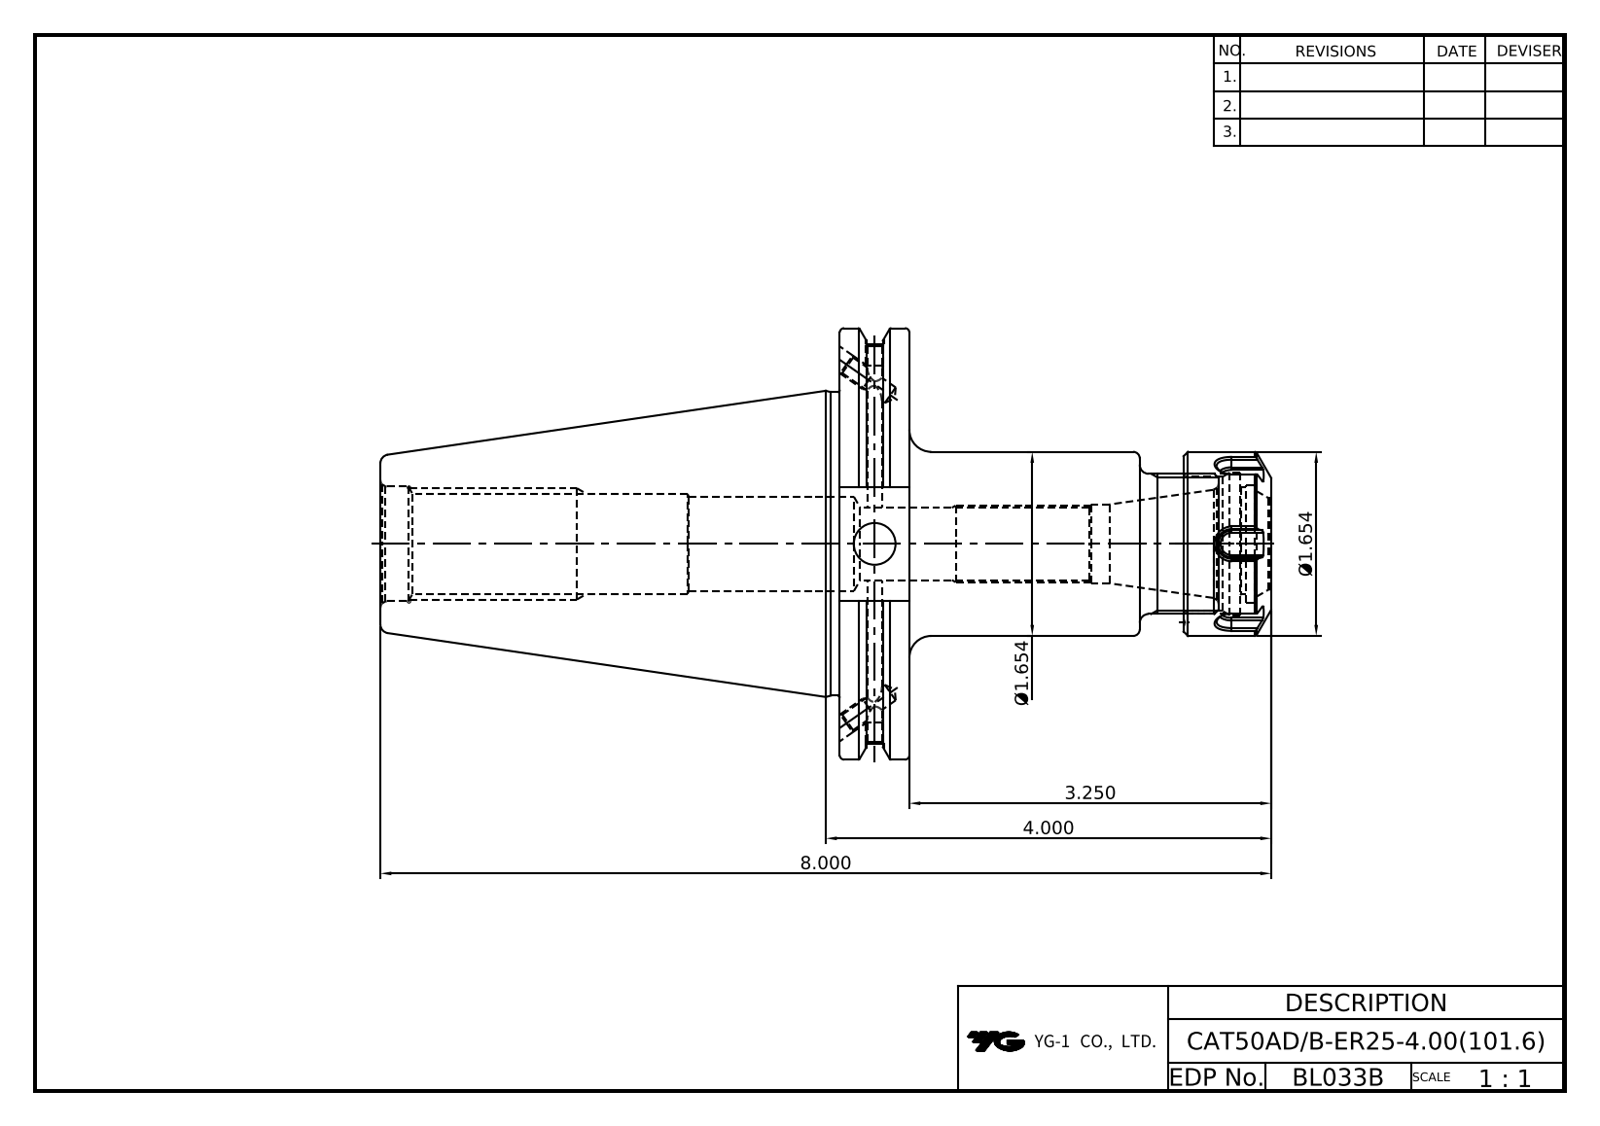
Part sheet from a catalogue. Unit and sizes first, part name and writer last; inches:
Units: inches
Overall size (bounding box): 8 × 3.875 × 3.728
Round holes (diameter × count): ⌀0.128 ×2, ⌀0.163 ×2, ⌀0.165 ×2, ⌀0.197 ×2, ⌀0.375 ×1, ⌀0.62 ×1, ⌀0.709 ×1, ⌀0.823 ×1, ⌀0.846 ×1, ⌀0.865 ×1, ⌀0.906 ×1, ⌀1.031 ×1
Round bosses / shafts (diameter × count): ⌀3.875 ×1, ⌀3.594 ×1, ⌀2.726 ×1, ⌀1.654 ×1, ⌀1.26 ×1
Partial cylindrical surfaces — rounded edges, fillets, slot ends (radius × count): R0.02 ×12
Main face-to-face distances: 0.625, 4.125, 4.75, 7.213, 3.088, 2.463, 7.72, 3.596, 2.97, 0.508
Volume: 24.53 in³ · Surface area: 98.84 in²
Bodies: 2 solids, 170 faces (73 planar, 45 cylindrical, 52 other)
Part name (STEP PRODUCT): LO-CAT50ADB-ER25-101.6_조립도; LO-CAT50ADB-ER25-101.6; ER25NUT
STEP written by: Autodesk Inventor 2020 (AUTOMOTIVE_DESIGN)
